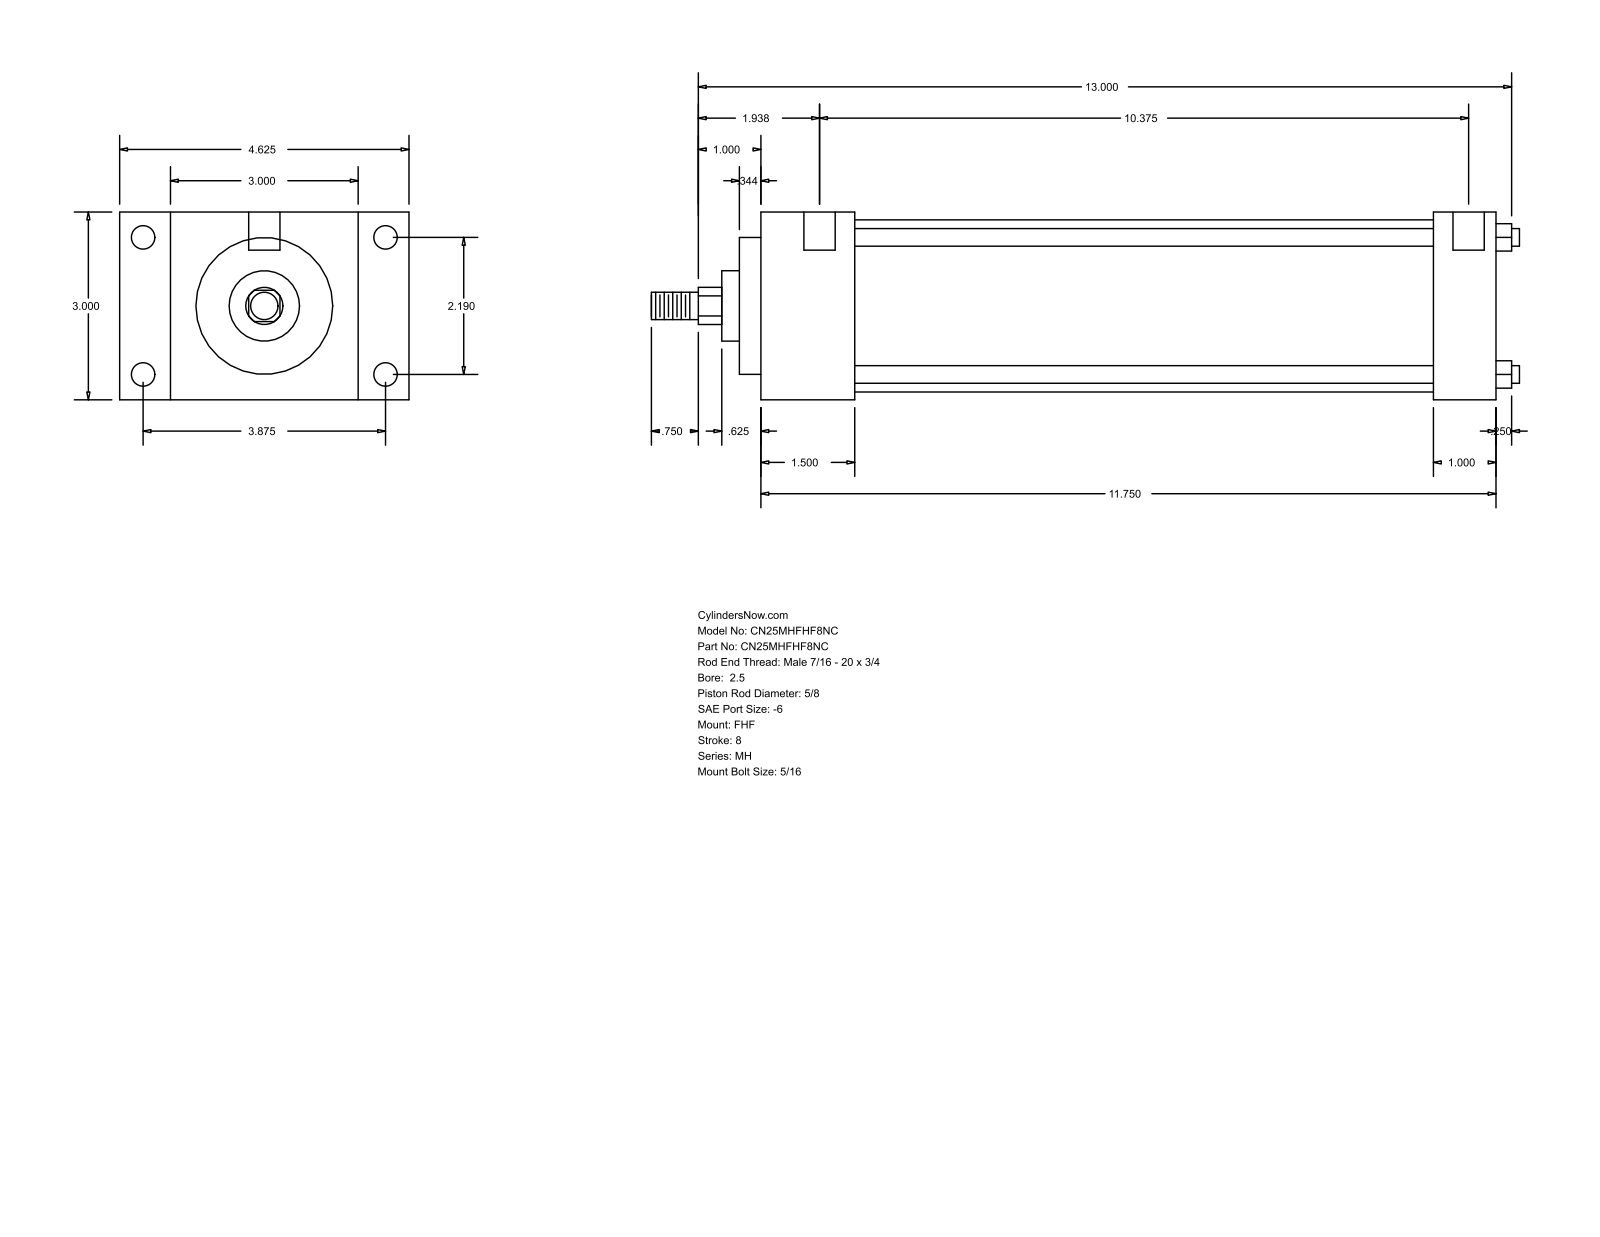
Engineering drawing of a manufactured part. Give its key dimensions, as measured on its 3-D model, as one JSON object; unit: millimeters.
{"part_name": "MH_FHF__0250_0.625", "step_written_by": "GSSL Pune (CONFIG_CONTROL_DESIGN)", "units": "millimeters", "bodies": {"solids": 0, "faces": 90, "planar": 61, "cylindrical": 29, "other": 0}, "overall_size": [352.43, 117.47, 76.2], "round_holes": [[5.56, 4], [9.53, 4], [12.7, 2]], "round_bosses_or_shafts": [[7.14, 4], [69.85, 1], [55.55, 1], [28.57, 1], [15.88, 1], [11.11, 1]], "partial_cylinders_radius": [[7.54, 1]], "face_to_face_distances": [76.2, 298.45, 38.1, 260.35, 20.64, 96.84, 117.48, 25.4, 273.05, 234.95], "hole_center_spacings": [55.62, 98.42, 113.05, 271.46, 3.17, 4.76, 263.53, 266.7]}
